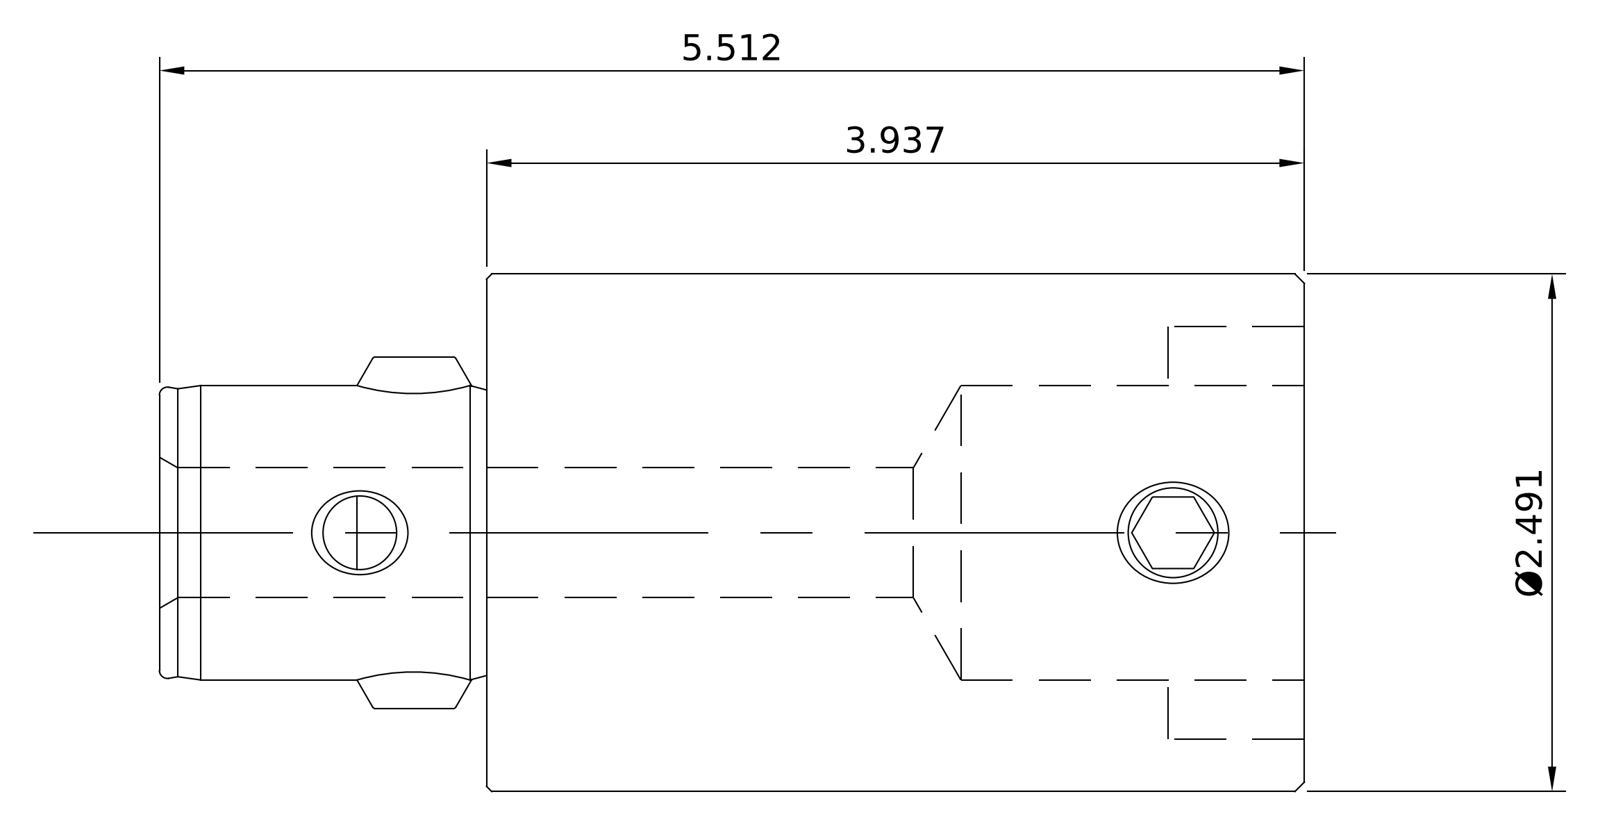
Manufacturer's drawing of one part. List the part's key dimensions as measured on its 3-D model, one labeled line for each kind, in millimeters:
Part name (STEP PRODUCT): 10.691.50X_10.691.506; 10.690.43X_10.690.436; 11.331.661; 11.331.661_11.331.661 (+1 more)
STEP written by: SolidWorks 2016 (AUTOMOTIVE_DESIGN)
Units: millimetres
Bodies: 4 solids, 141 faces (38 planar, 47 cylindrical, 56 other)
Overall size (bounding box): 140 × 63.27 × 63.27
Volume: 278 216 mm³ · Surface area: 45 556 mm²
Round holes (diameter × count): ⌀5 ×1, ⌀9 ×1, ⌀10.2 ×1, ⌀12.3 ×1, ⌀14 ×1, ⌀16 ×1, ⌀19 ×1, ⌀26 ×1, ⌀36 ×1, ⌀36.5 ×1
Round bosses / shafts (diameter × count): ⌀63.27 ×1, ⌀62.87 ×1, ⌀13.9 ×1, ⌀12 ×1, ⌀11.9 ×1, ⌀9.9 ×1
Partial cylindrical surfaces — rounded edges, fillets, slot ends (radius × count): R5.5 ×2, R18 ×1
Main face-to-face distances: 100, 40, 140, 95, 55, 45, 30.7, 123.4, 83.4, 28.4
Hole centre spacings: 25, 99.45
